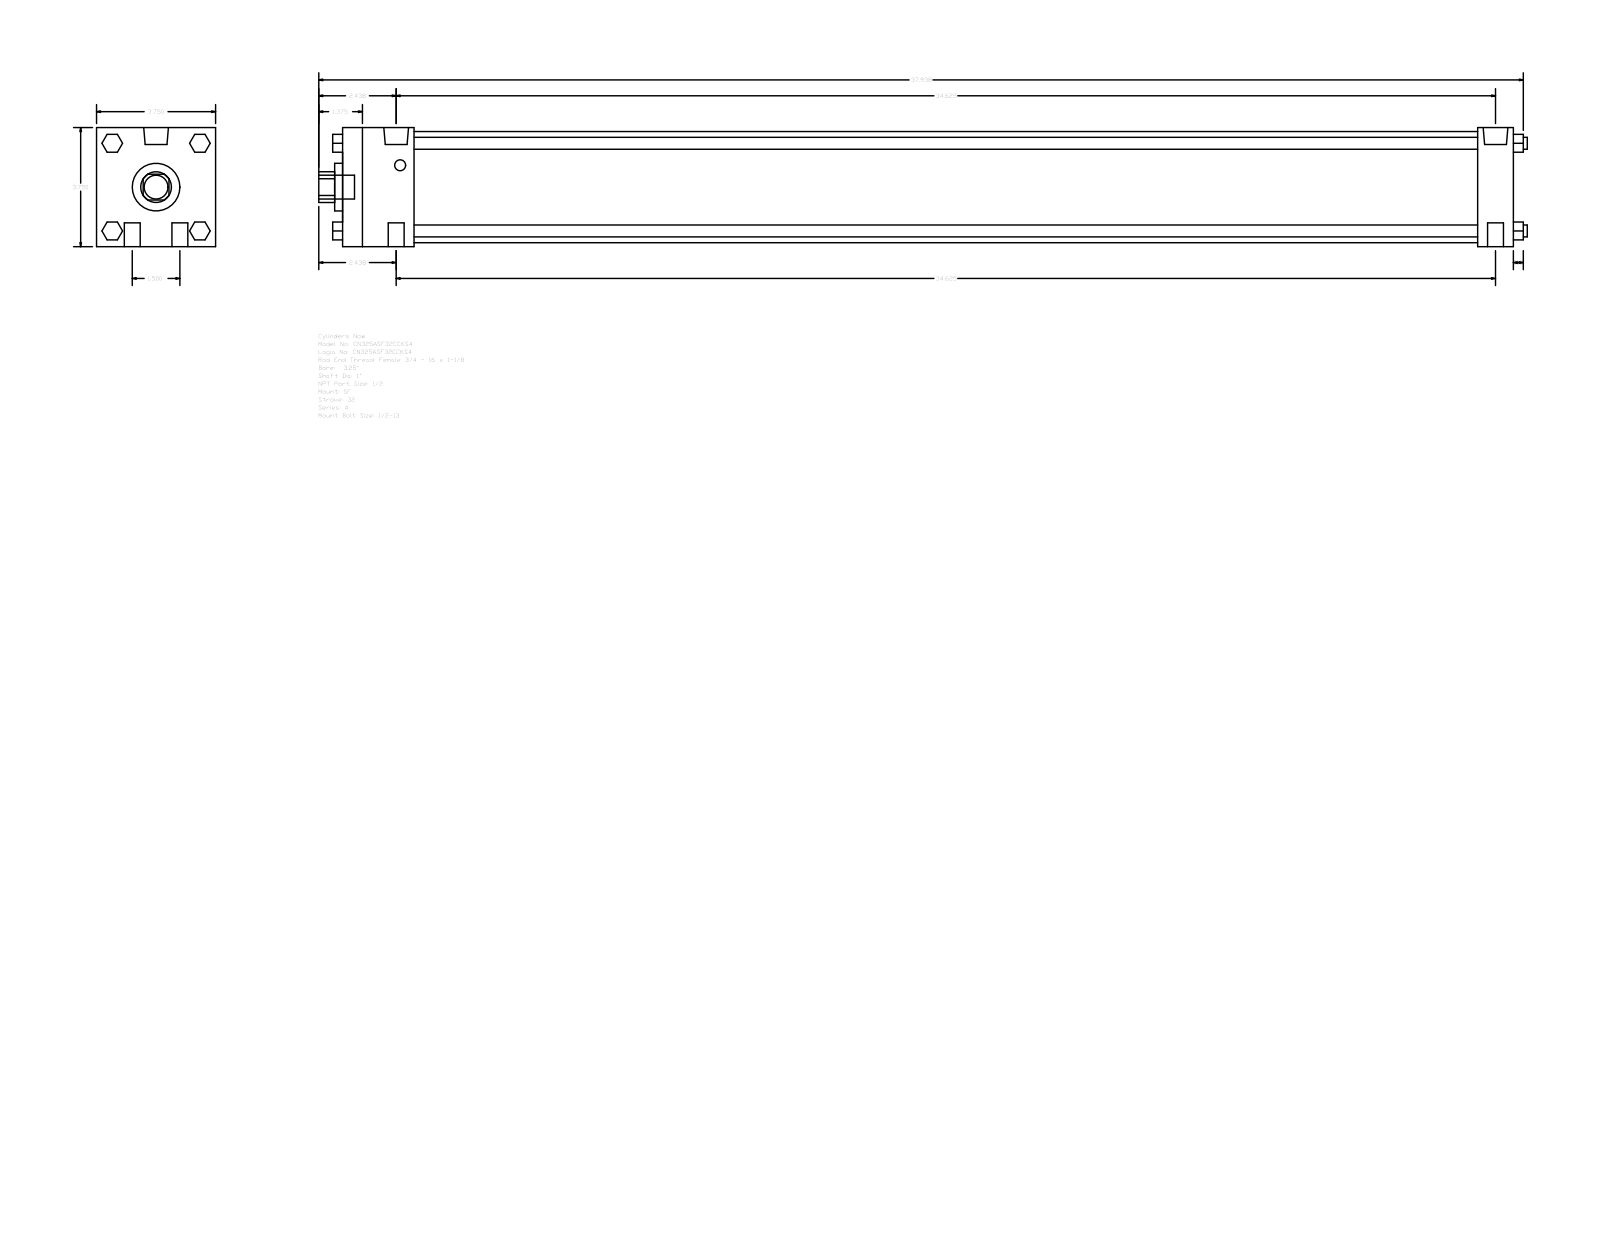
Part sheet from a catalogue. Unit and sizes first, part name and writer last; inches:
Units: inches
Overall size (bounding box): 38.063 × 3.75 × 3.75
Round holes (diameter × count): ⌀1 ×1, ⌀1.5 ×1, ⌀3.5 ×1
Round bosses / shafts (diameter × count): ⌀0.5 ×4, ⌀0.375 ×4, ⌀0.778 ×2, ⌀0.344 ×2, ⌀0.75 ×1
Partial cylindrical surfaces — rounded edges, fillets, slot ends (radius × count): R0.484 ×1
Main face-to-face distances: 3.75, 36.875, 1.125, 35.75, 2.25, 33.5, 34.625, 0.562, 1.38, 2.39
Bodies: 0 solids, 124 faces (94 planar, 30 cylindrical, 0 other)
Part name (STEP PRODUCT): A_SF__0325_1
STEP written by: GSSL Pune (CONFIG_CONTROL_DESIGN)
